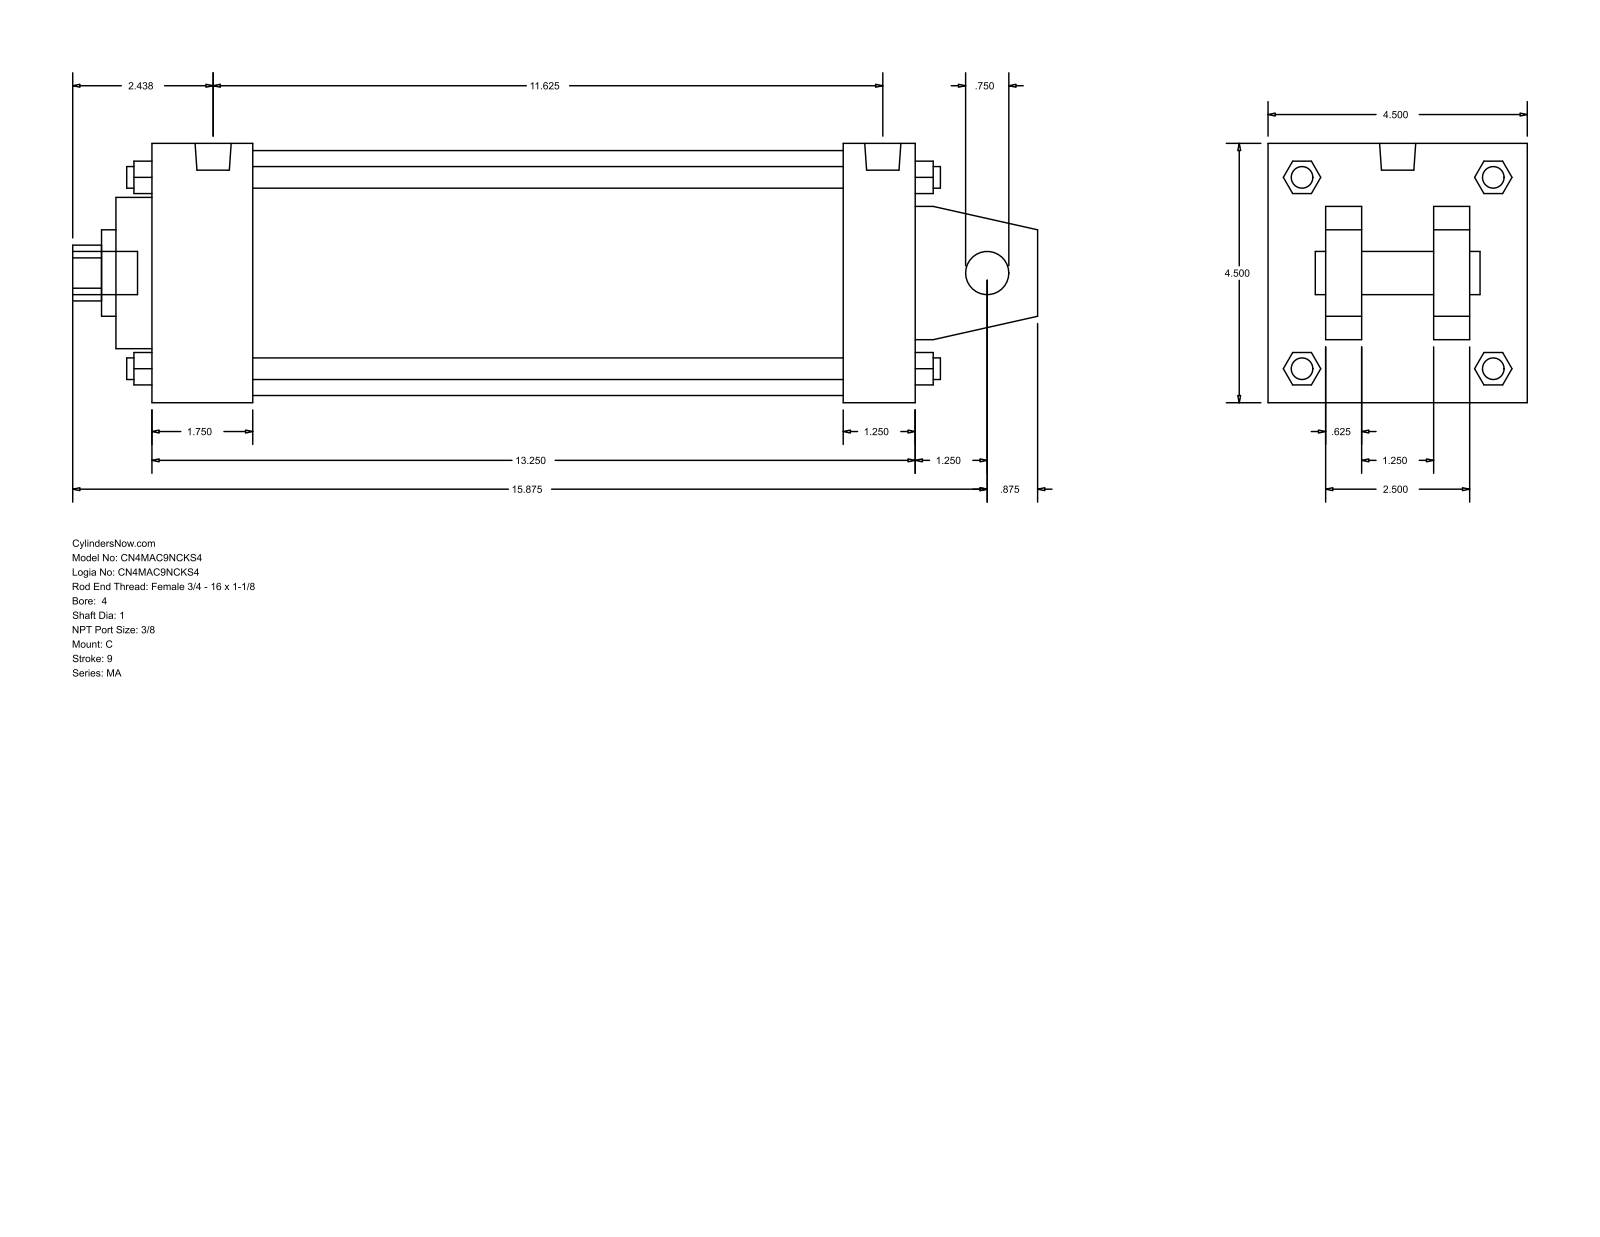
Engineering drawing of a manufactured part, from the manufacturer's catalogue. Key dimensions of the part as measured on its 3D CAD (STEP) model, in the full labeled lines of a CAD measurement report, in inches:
Part name (STEP PRODUCT): MA_C__0400_1
STEP written by: GSSL Pune (CONFIG_CONTROL_DESIGN)
Units: inches
Bodies: 0 solids, 141 faces (109 planar, 32 cylindrical, 0 other)
Overall size (bounding box): 16.75 × 4.5 × 4.5
Round holes (diameter × count): ⌀0.75 ×1, ⌀1 ×1, ⌀1.5 ×1, ⌀2.625 ×1, ⌀4.25 ×1
Round bosses / shafts (diameter × count): ⌀0.437 ×4, ⌀0.375 ×4, ⌀0.627 ×2, ⌀0.75 ×1
Partial cylindrical surfaces — rounded edges, fillets, slot ends (radius × count): R0.484 ×1
Main face-to-face distances: 4.5, 13.25, 0.625, 2.875, 1.625, 1, 3.5, 1.875, 12, 1.25
